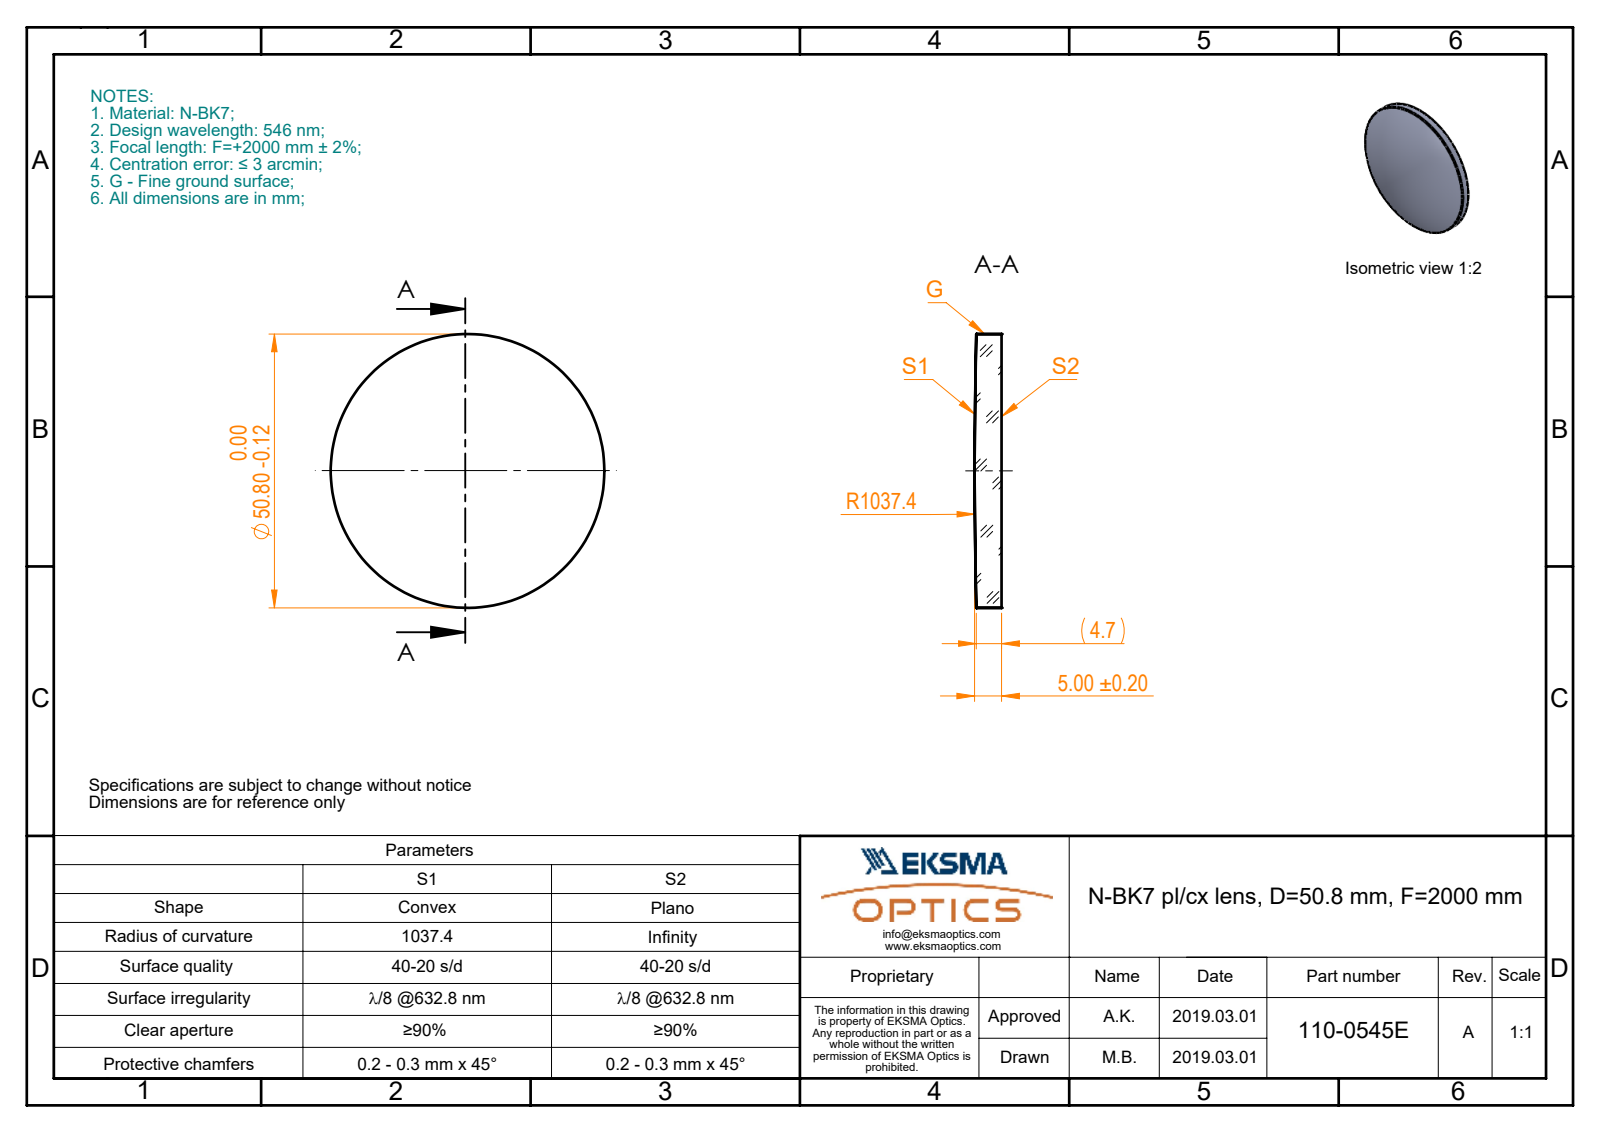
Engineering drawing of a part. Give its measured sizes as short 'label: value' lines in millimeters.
name: 110-0545E BK7 pl-cx 50.8 F2000
written by: SolidWorks 2017 (CONFIG_CONTROL_DESIGN)
unit: mm
bodies: 1 solid, 5 faces (1 planar, 2 cylindrical, 2 other)
size: 50.8 × 50.8 × 5
volume: 9 819 mm³; area: 4 802 mm²
bosses: 1× ⌀50.8
